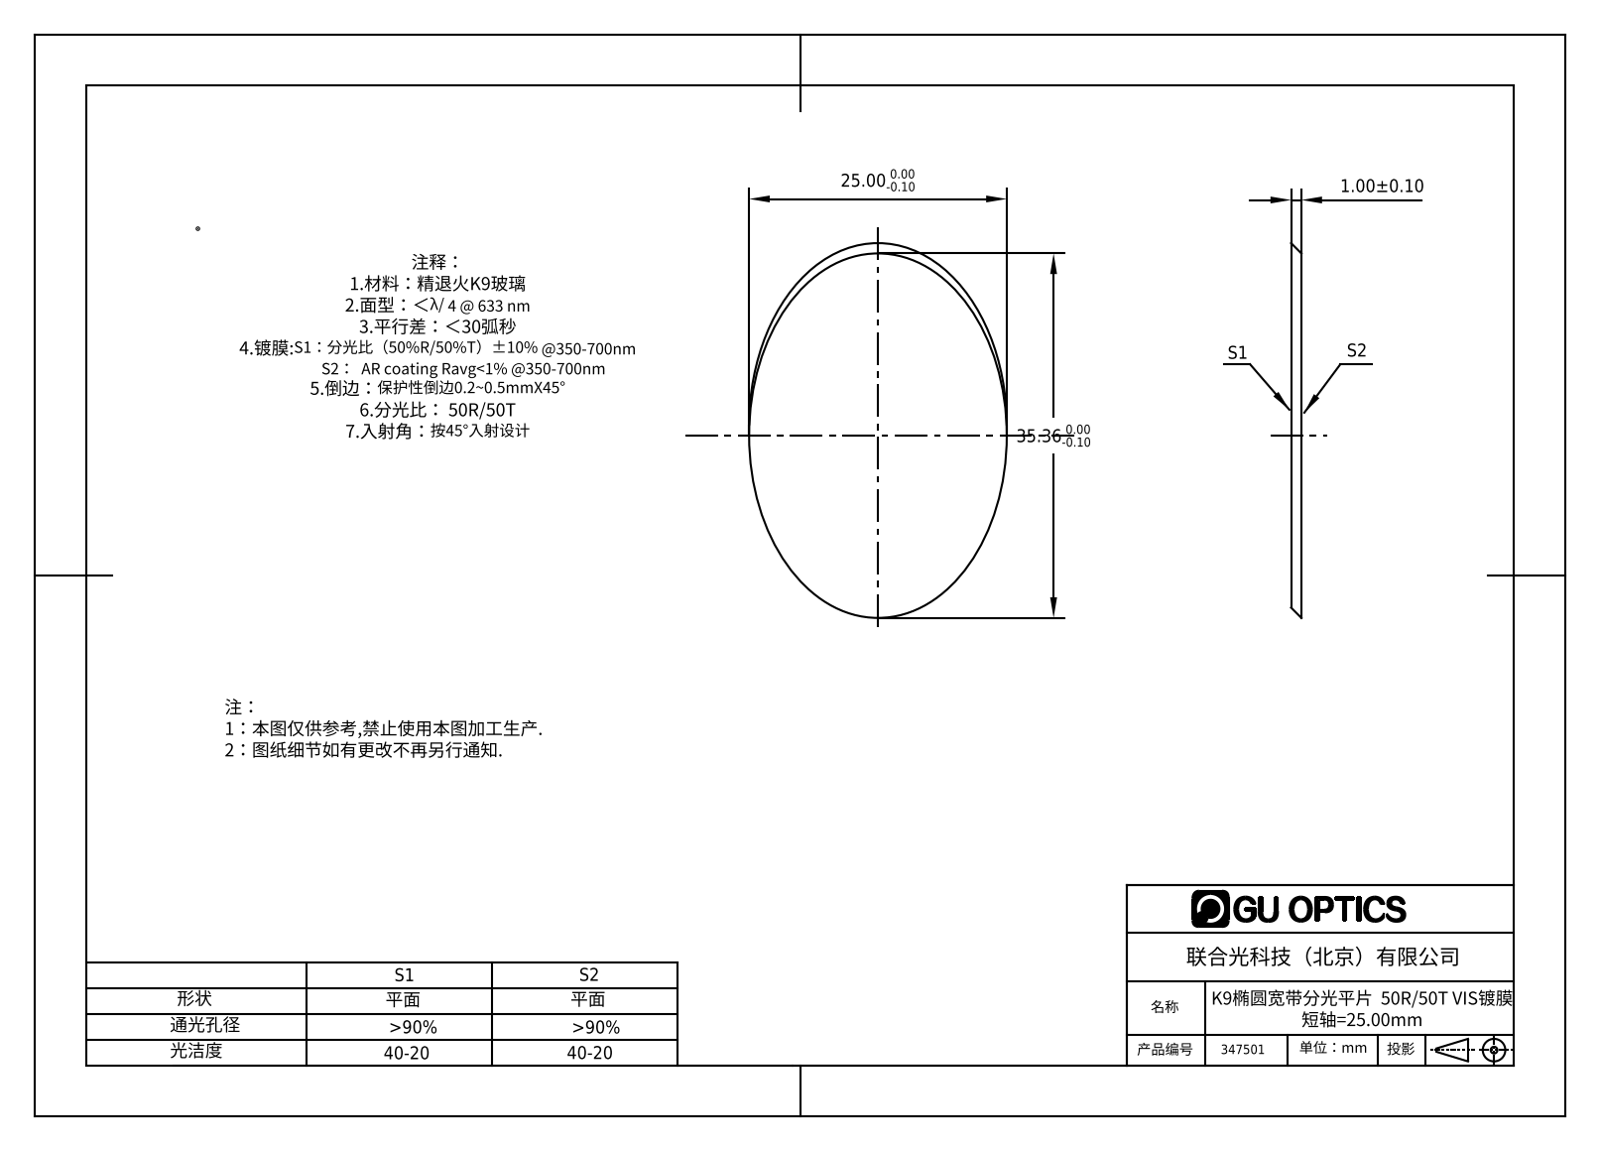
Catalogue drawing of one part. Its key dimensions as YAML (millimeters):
part_name: "347501"
step_written_by: "SolidWorks 2019 (CONFIG_CONTROL_DESIGN)"
units: millimeters
bodies: {solids: 1, faces: 4, planar: 2, cylindrical: 2, other: 0}
overall_size: [26.41, 25, 25]
volume: 694
surface_area: 1500
round_bosses_or_shafts:
  - {diameter: 25, count: 1}
face_to_face_distances: [1]
